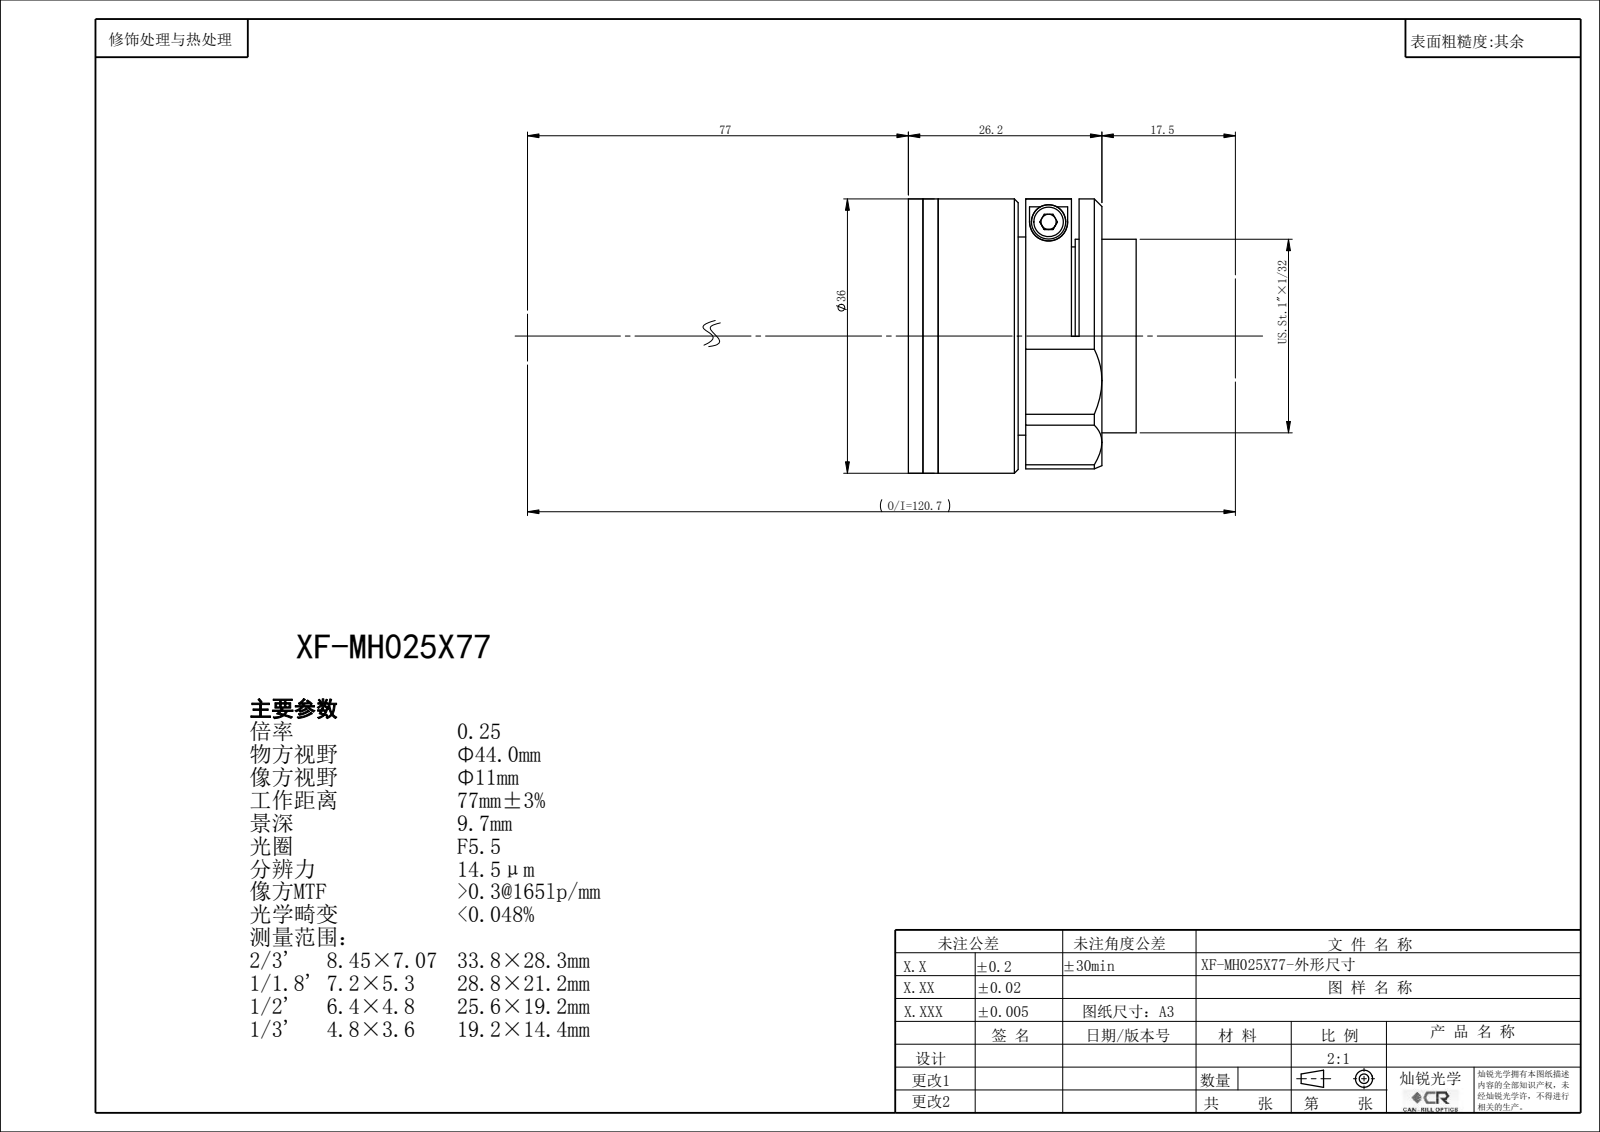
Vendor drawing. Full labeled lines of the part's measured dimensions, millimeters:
Part name (STEP PRODUCT): XF-MH025X77
STEP written by: SolidWorks 2022 (CONFIG_CONTROL_DESIGN)
Units: millimetres
Bodies: 0 solids, 111 faces (51 planar, 50 cylindrical, 10 other)
Overall size (bounding box): 36 × 36 × 30.17
Round holes (diameter × count): ⌀2.5 ×3, ⌀7 ×1, ⌀8.4 ×1, ⌀10 ×1, ⌀12 ×1, ⌀14 ×1, ⌀16 ×1, ⌀18 ×1, ⌀20 ×1, ⌀21.5 ×1, ⌀22 ×1, ⌀24 ×1
Round bosses / shafts (diameter × count): ⌀36 ×1, ⌀34 ×1, ⌀25.4 ×1, ⌀9 ×1
Main face-to-face distances: 2, 3.91, 1.91, 24.26, 22.26, 26.17, 4, 1, 1.5, 24.67
